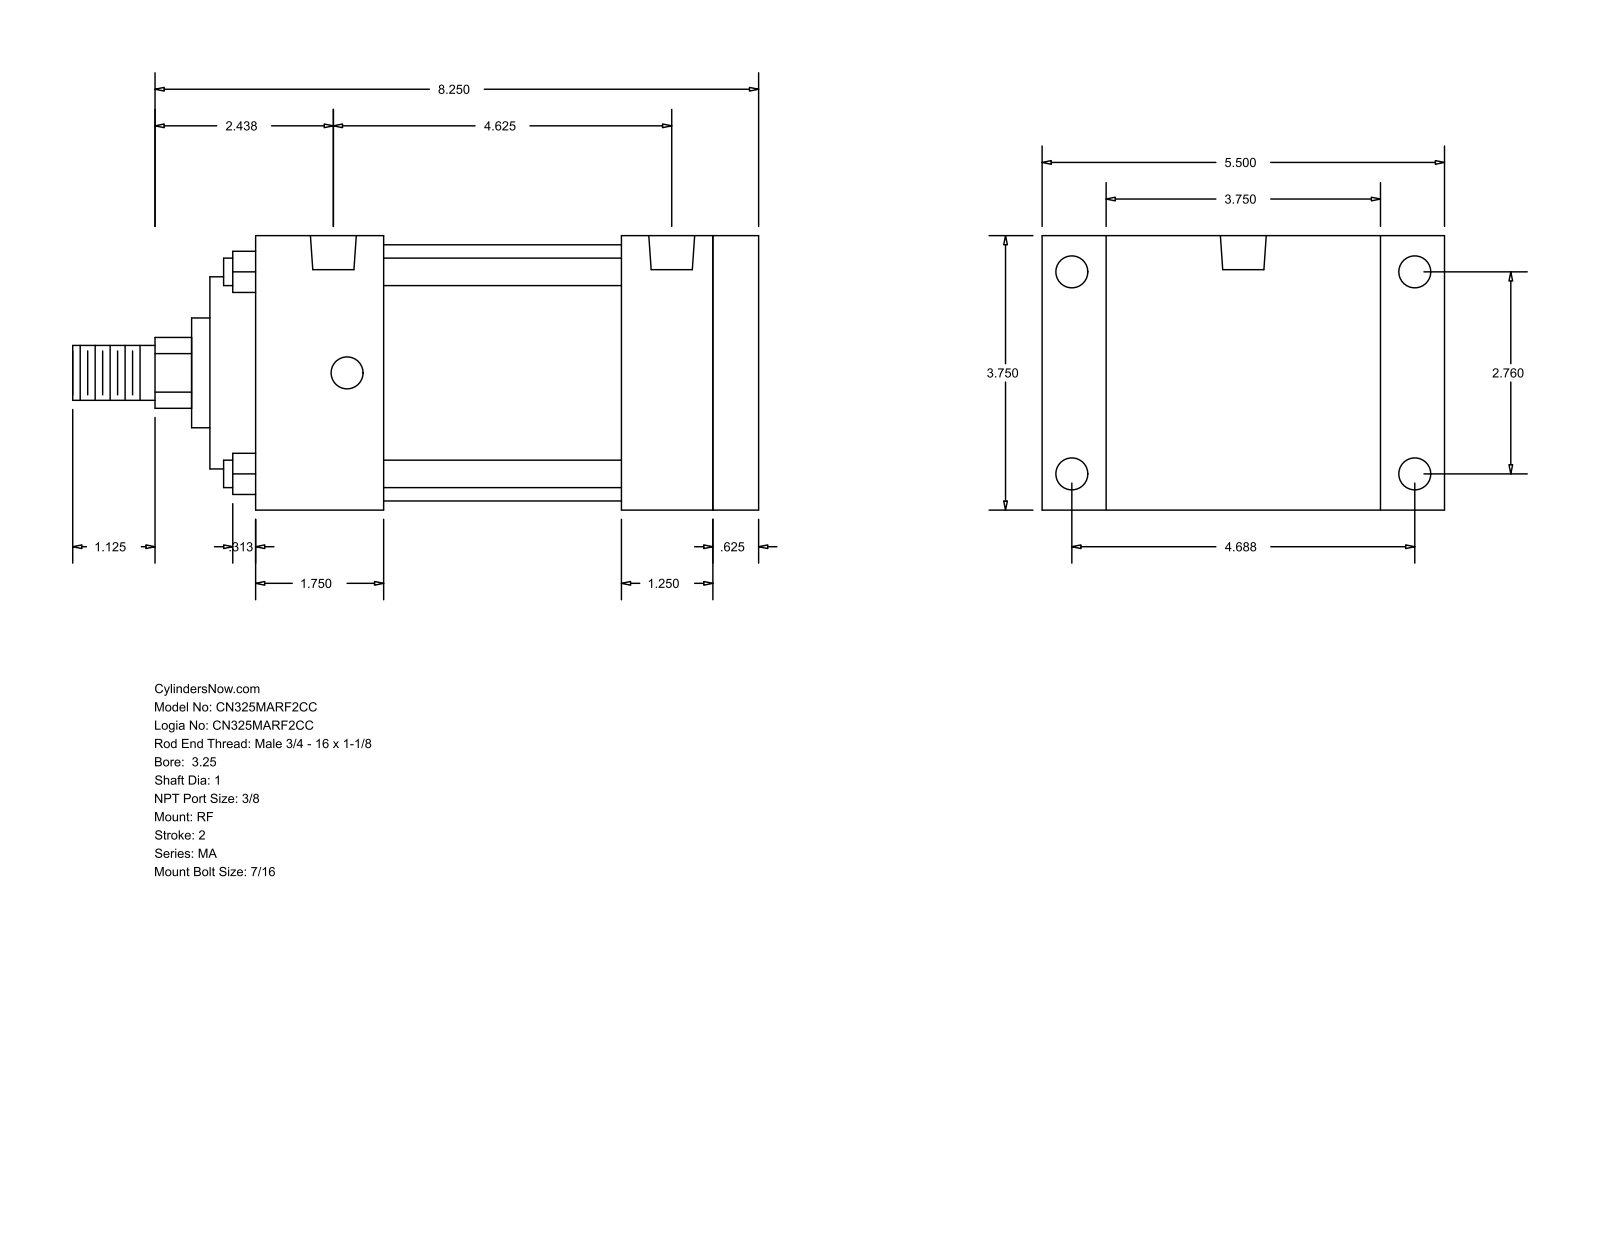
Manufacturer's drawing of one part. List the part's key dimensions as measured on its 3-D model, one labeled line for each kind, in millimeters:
Part name (STEP PRODUCT): MA_RF__0325_1
STEP written by: GSSL Pune (CONFIG_CONTROL_DESIGN)
Units: millimetres
Bodies: 0 solids, 94 faces (65 planar, 29 cylindrical, 0 other)
Overall size (bounding box): 238.12 × 139.7 × 95.25
Round holes (diameter × count): ⌀11.11 ×8, ⌀15.93 ×2
Round bosses / shafts (diameter × count): ⌀9.53 ×4, ⌀88.9 ×1, ⌀66.67 ×1, ⌀38.1 ×1, ⌀25.4 ×1, ⌀19.05 ×1
Partial cylindrical surfaces — rounded edges, fillets, slot ends (radius × count): R12.29 ×1
Main face-to-face distances: 95.24, 174.63, 15.87, 158.76, 22.23, 117.47, 47.62, 190.5, 127.01, 31.75
Hole centre spacings: 70.1, 107.95, 119.06, 138.16, 4.76, 4.77, 112.71, 112.72
